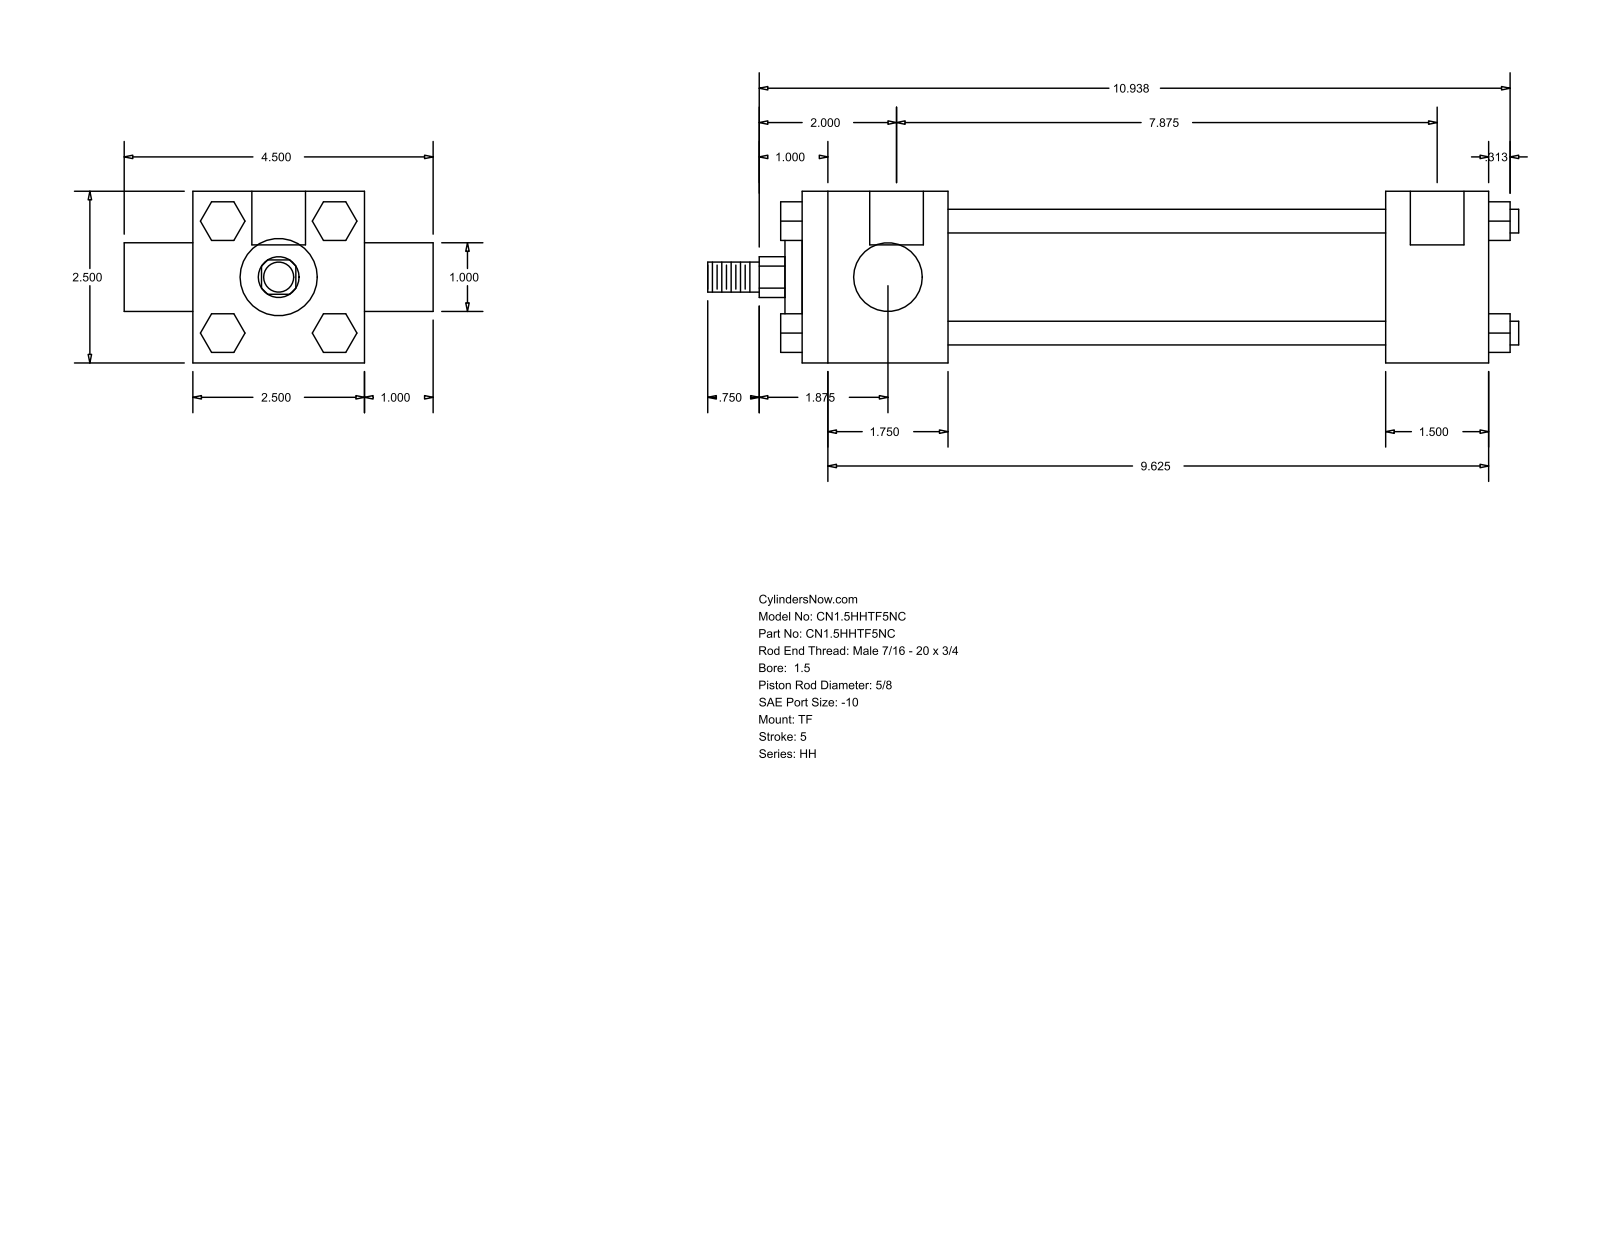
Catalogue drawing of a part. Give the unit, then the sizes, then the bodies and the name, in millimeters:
Units: millimetres
Overall size (bounding box): 300.04 × 114.3 × 63.5
Round holes (diameter × count): ⌀5.56 ×3, ⌀19.84 ×2
Round bosses / shafts (diameter × count): ⌀8.76 ×4, ⌀44.45 ×1, ⌀28.57 ×1, ⌀25.4 ×1, ⌀15.88 ×1, ⌀11.11 ×1
Partial cylindrical surfaces — rounded edges, fillets, slot ends (radius × count): R7.54 ×1
Main face-to-face distances: 63.5, 254, 38.1, 53.97, 200.03, 215.9, 161.93, 25.4, 88.9, 20.7
Hole centre spacings: 1.59, 201.61, 200.02, 203.2
Bodies: 0 solids, 120 faces (92 planar, 28 cylindrical, 0 other)
Part name (STEP PRODUCT): HH_TF__0150_0.625
STEP written by: GSSL Pune (CONFIG_CONTROL_DESIGN)
